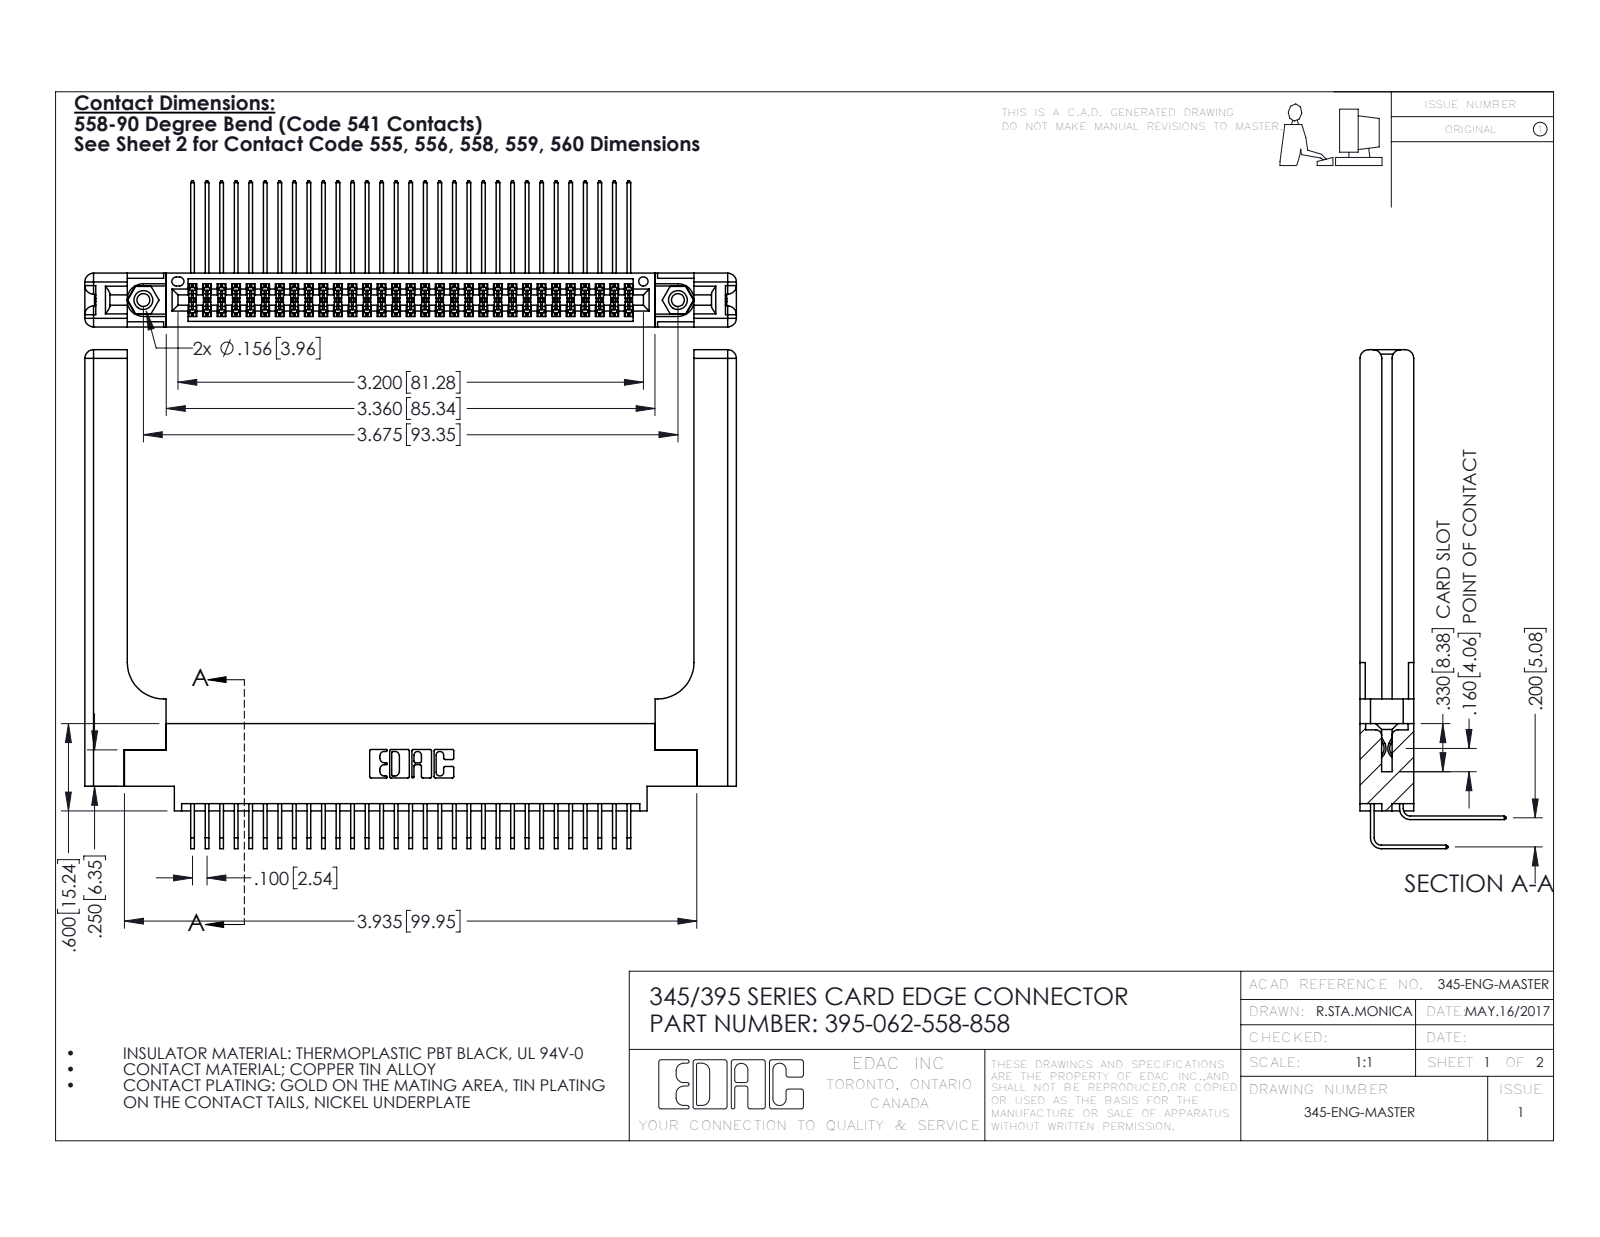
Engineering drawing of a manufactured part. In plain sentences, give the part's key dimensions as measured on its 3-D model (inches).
The part is named "345-292-001_558 559 Tail - 1; 395-062-558-858; 345-292-001_558 Tail - 2; 345-250-001_345-250-001-102 (+2 more)". Its 3-D file was written by "SolidWorks 2016 (CONFIG_CONTROL_DESIGN)". It is 67 solids with 3610 faces: 2402 planar, 1148 cylindrical and 60 other. Overall it measures 4.479 by 3.429 by 1.005 inches. Its volume is 1.2 cubic inches and its surface area 35.99 square inches. Round holes: 2 of diameter 0.089, 2 of diameter 0.125, 2 of diameter 0.156, 1 of diameter 0.064. Round bosses or shafts: 2 of diameter 0.155. Partial cylindrical surfaces (rounded edges, fillets, slot ends): 94 of radius 0.006, 22 of radius 0.01, 16 of radius 0.06, 6 of radius 0.007, 6 of radius 0.031, 3 of radius 0.026, 2 of radius 0.014, 2 of radius 0.019. The main face-to-face distances are 0.37, 0.072, 0.298, 0.2, 0.098, 0.272, 0.025, 0.225, 0.148, 0.15. The hole center spacings are 0.27, 3.44, 3.675.
